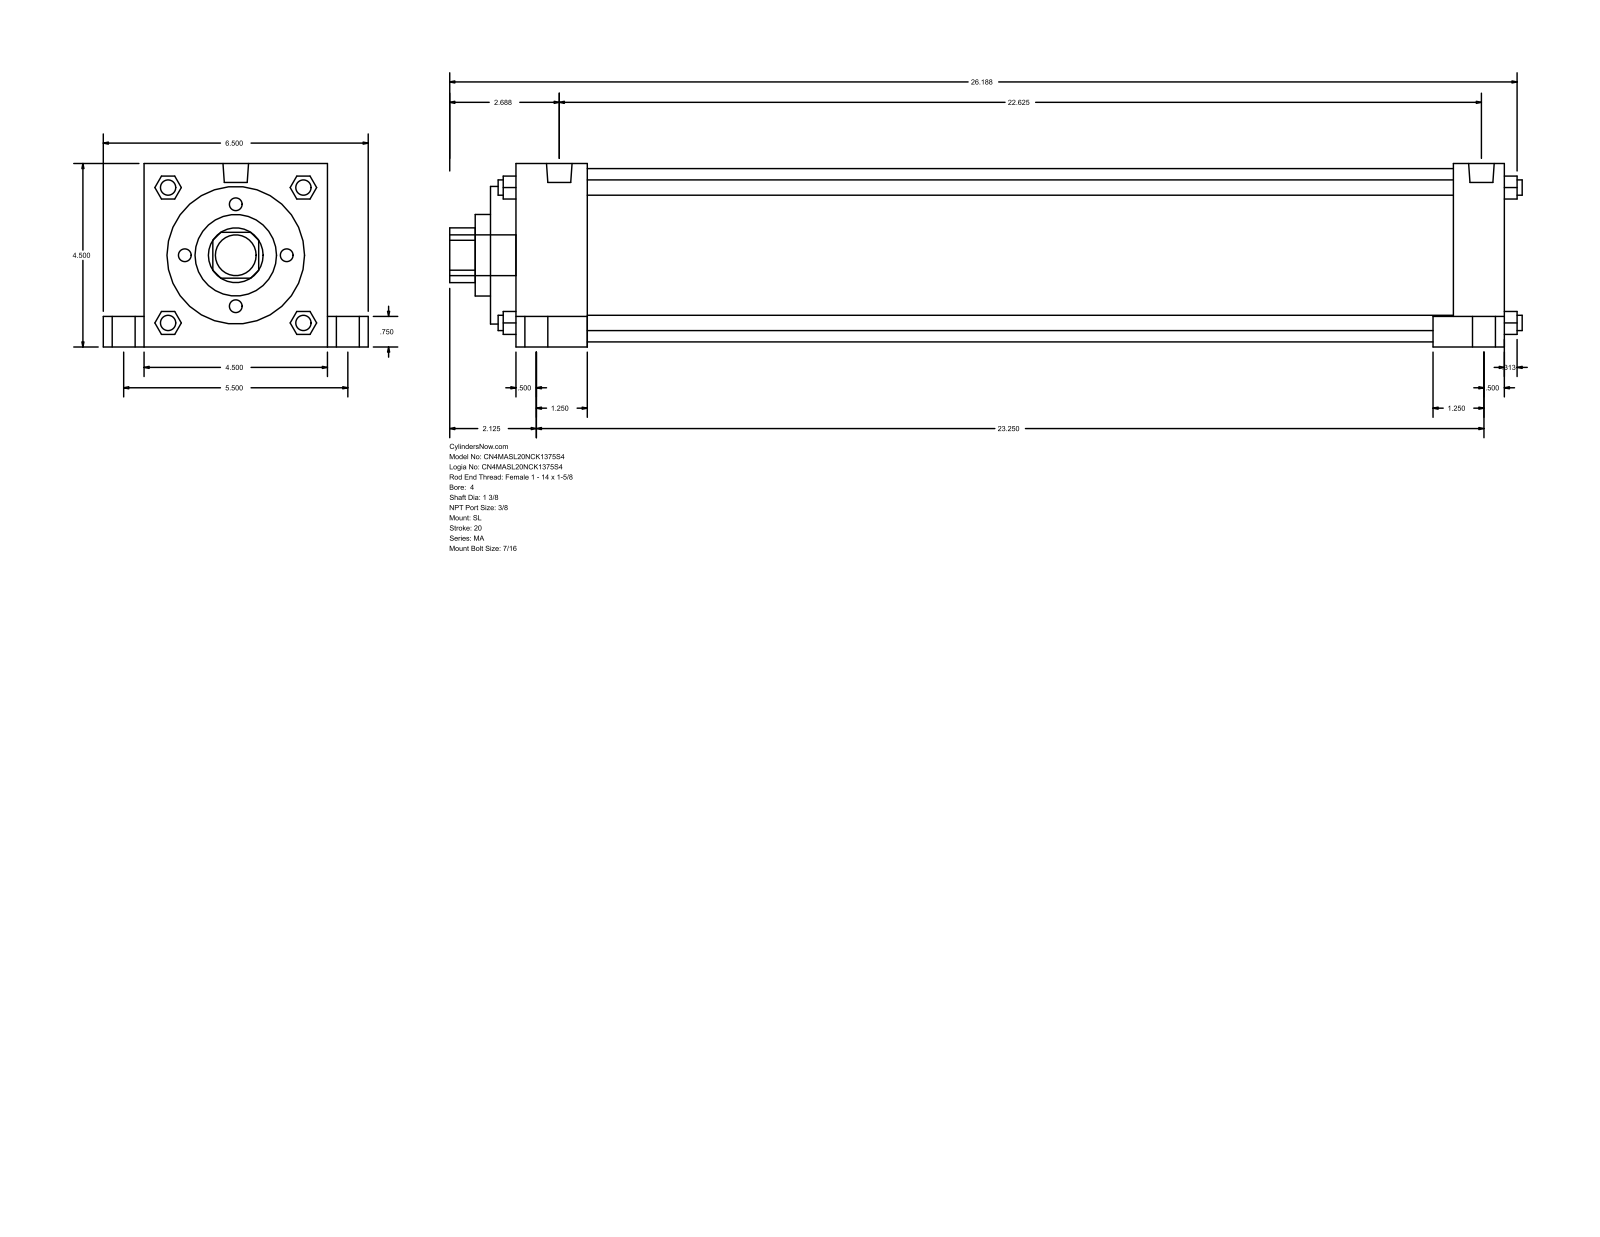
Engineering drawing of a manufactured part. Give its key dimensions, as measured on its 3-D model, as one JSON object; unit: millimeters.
{"part_name": "MA_SL__0400_1.375", "step_written_by": "GSSL Pune (CONFIG_CONTROL_DESIGN)", "units": "millimeters", "bodies": {"solids": 0, "faces": 150, "planar": 113, "cylindrical": 37, "other": 0}, "overall_size": [668.34, 165.1, 114.3], "round_holes": [[34.92, 1], [50.8, 1], [85.72, 1], [107.95, 1]], "round_bosses_or_shafts": [[20.64, 4], [14.29, 4], [11.11, 4], [9.53, 4], [15.93, 2], [25.4, 1]], "partial_cylinders_radius": [[17.06, 1]], "face_to_face_distances": [114.3, 615.96, 15.87, 631.83, 60.32, 44.45, 571.51, 600.08, 584.21, 539.76]}
